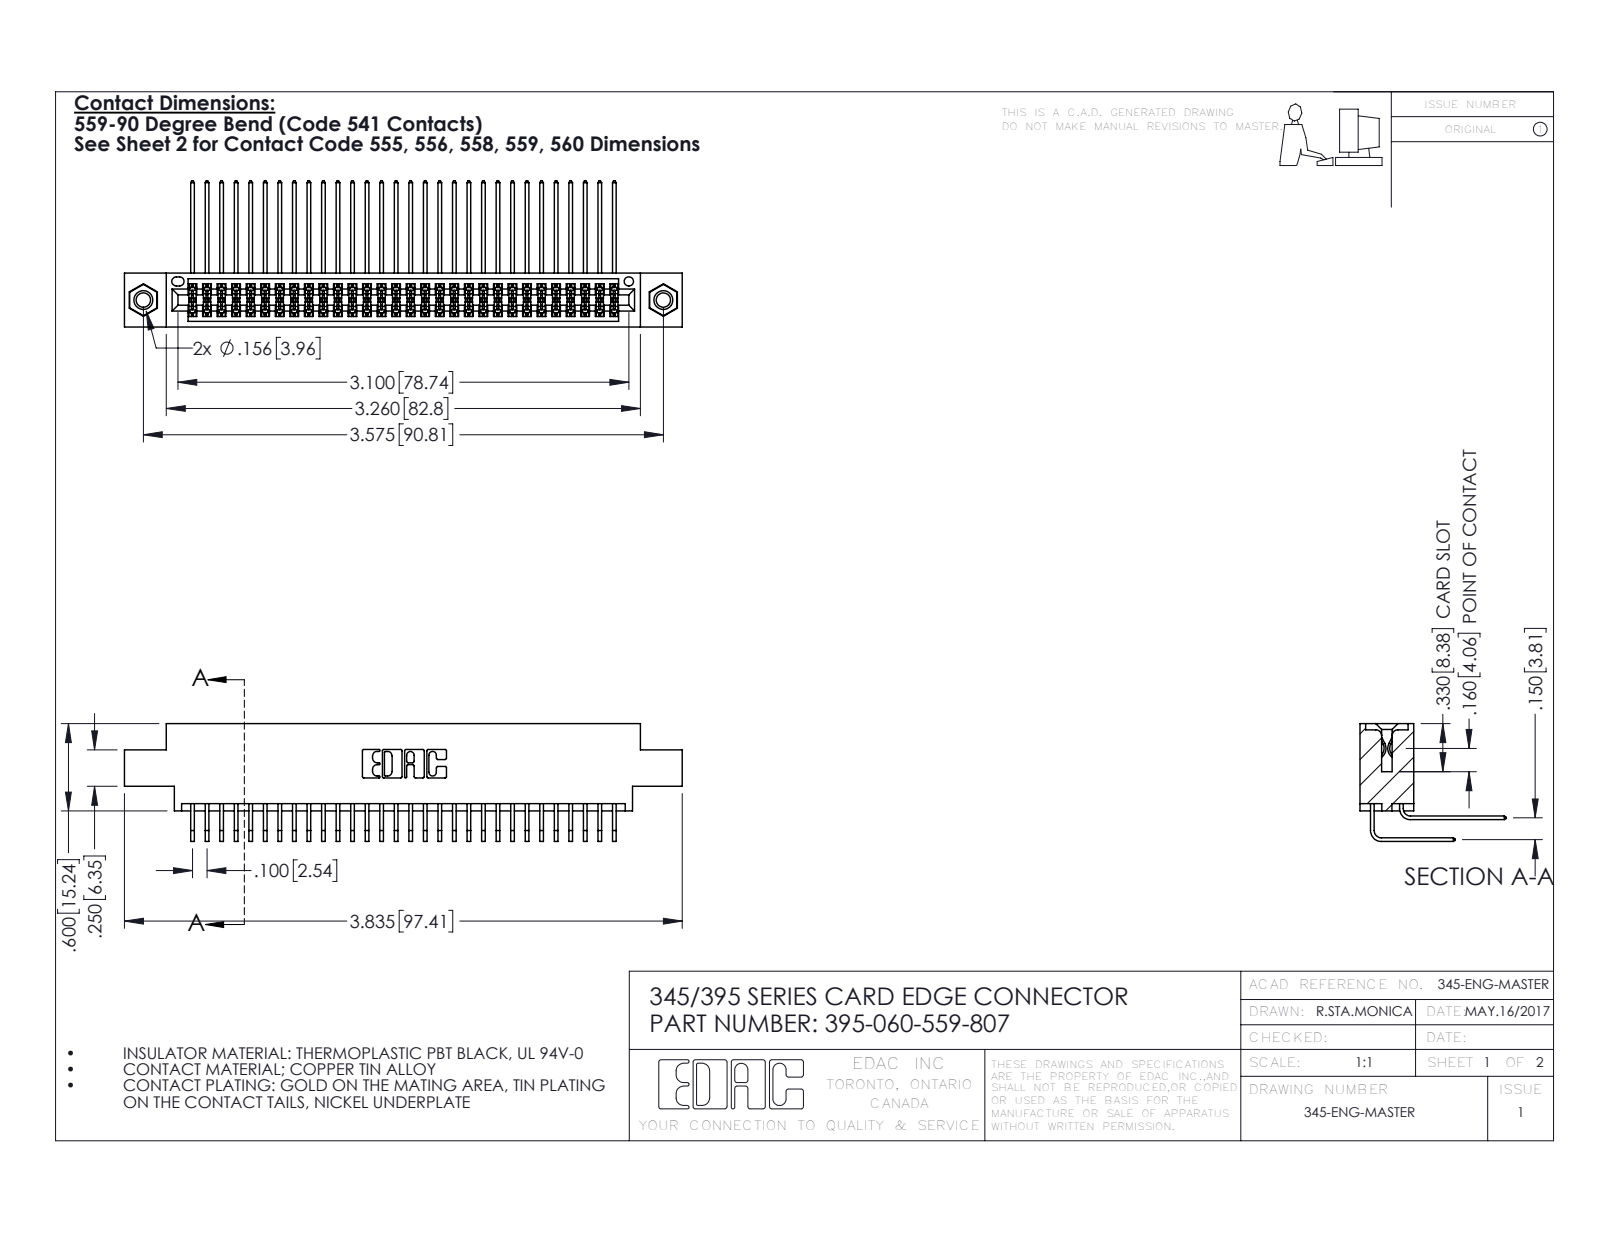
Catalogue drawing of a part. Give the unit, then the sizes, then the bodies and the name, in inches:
Units: inches
Overall size (bounding box): 3.835 × 1.005 × 0.809
Round holes (diameter × count): ⌀0.098 ×2, ⌀0.125 ×2, ⌀0.156 ×2, ⌀0.064 ×1
Round bosses / shafts (diameter × count): ⌀0.155 ×2
Partial cylindrical surfaces — rounded edges, fillets, slot ends (radius × count): R0.006 ×90, R0.01 ×22, R0.007 ×6, R0.031 ×6, R0.026 ×3, R0.014 ×2, R0.019 ×2, R0.022 ×2
Main face-to-face distances: 0.072, 0.298, 0.37, 0.2, 0.098, 0.272, 0.025, 0.225, 0.175, 0.15
Hole centre spacings: 0.27, 3.34, 3.575
Volume: 0.584 in³ · Surface area: 24.36 in²
Bodies: 63 solids, 3310 faces (2216 planar, 1078 cylindrical, 16 other)
Part name (STEP PRODUCT): 345-292-001_559 Tail - 2; 345 Part_0.170 Offset - 0.156 Dia-TI; 395-060-559-807; 345-250-001_345-250-005-103 (+1 more)
STEP written by: SolidWorks 2016 (CONFIG_CONTROL_DESIGN)
